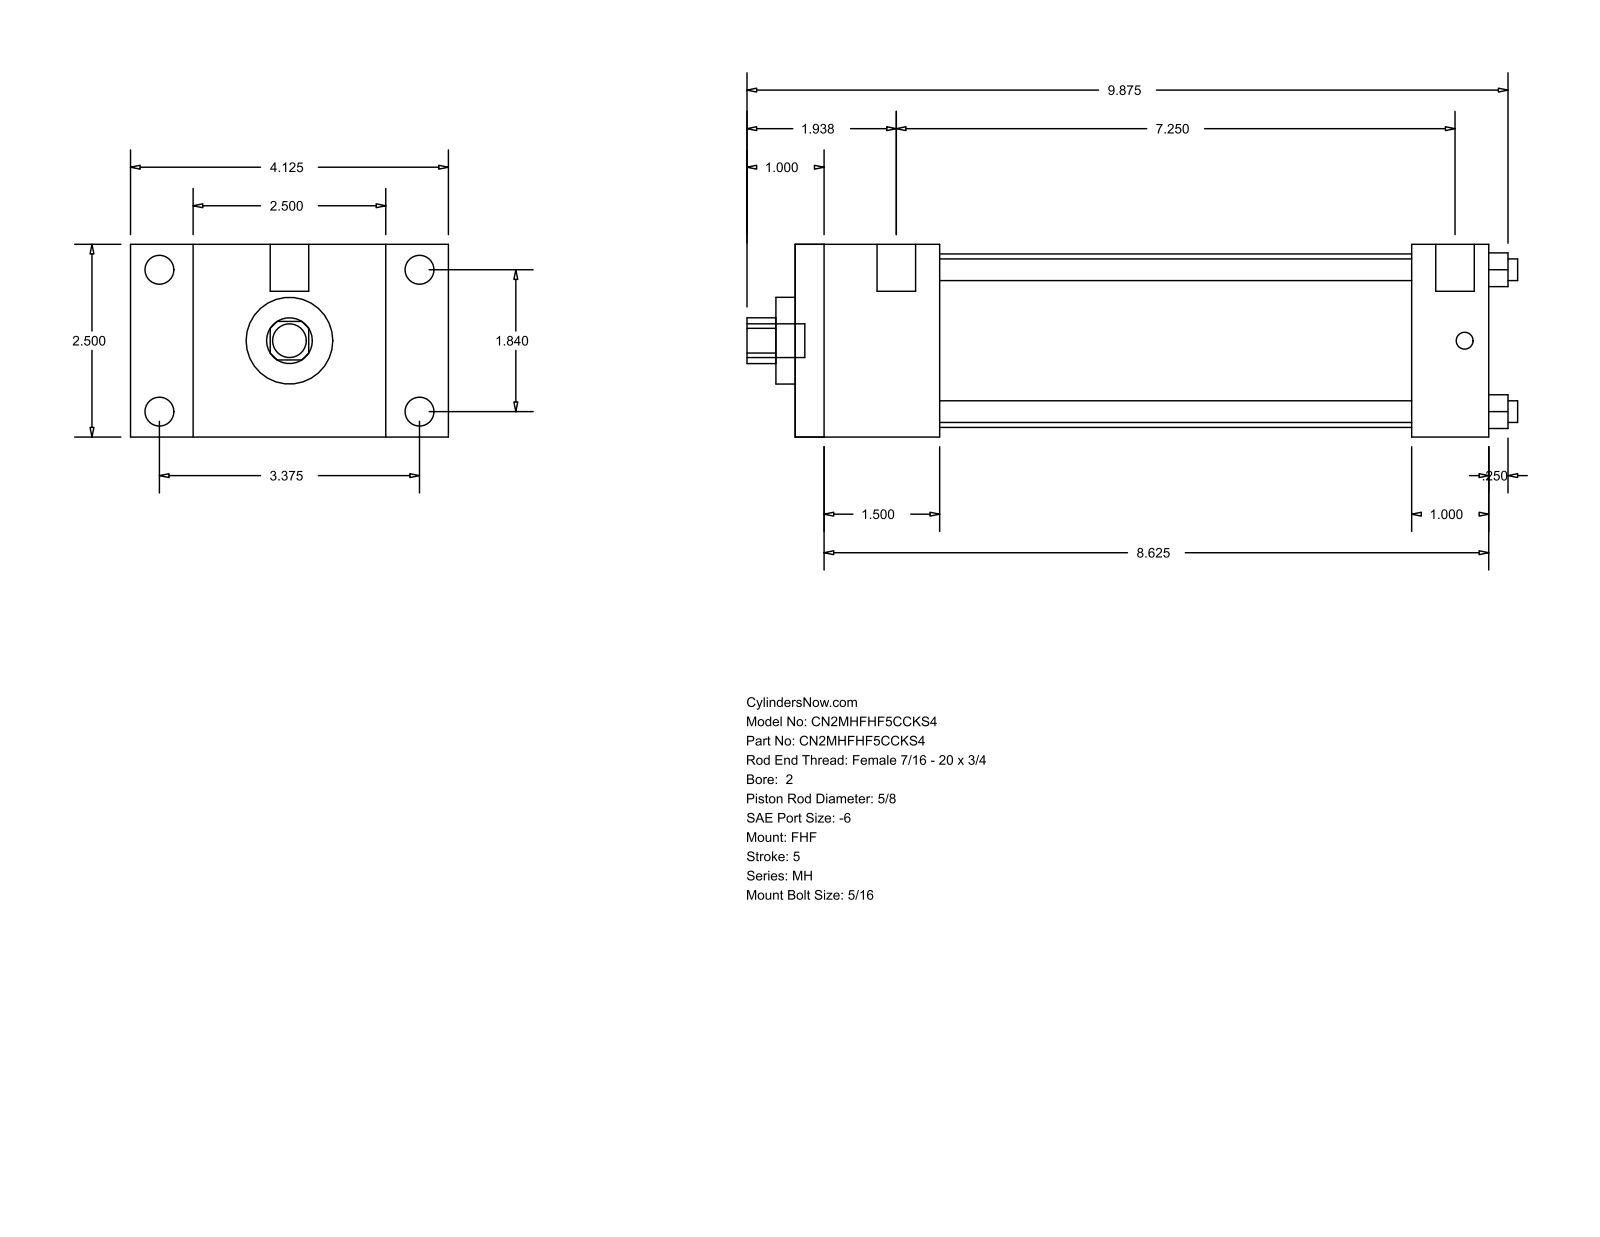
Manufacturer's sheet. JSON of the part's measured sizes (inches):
{"part_name": "MH_FHF__0200_0.625", "step_written_by": "GSSL Pune (CONFIG_CONTROL_DESIGN)", "units": "inches", "bodies": {"solids": 0, "faces": 88, "planar": 60, "cylindrical": 28, "other": 0}, "overall_size": [10, 4.125, 2.5], "round_holes": [[0.281, 4], [0.625, 1], [1.125, 1], [2.25, 1]], "round_bosses_or_shafts": [[0.375, 4], [0.219, 4], [0.5, 2], [0.437, 1]], "partial_cylinders_radius": [[0.297, 1]], "face_to_face_distances": [2.5, 1.875, 9, 7.125, 0.813, 3.313, 4.125, 1, 8, 6.125], "hole_center_spacings": [1.301, 1.84, 2.602]}
